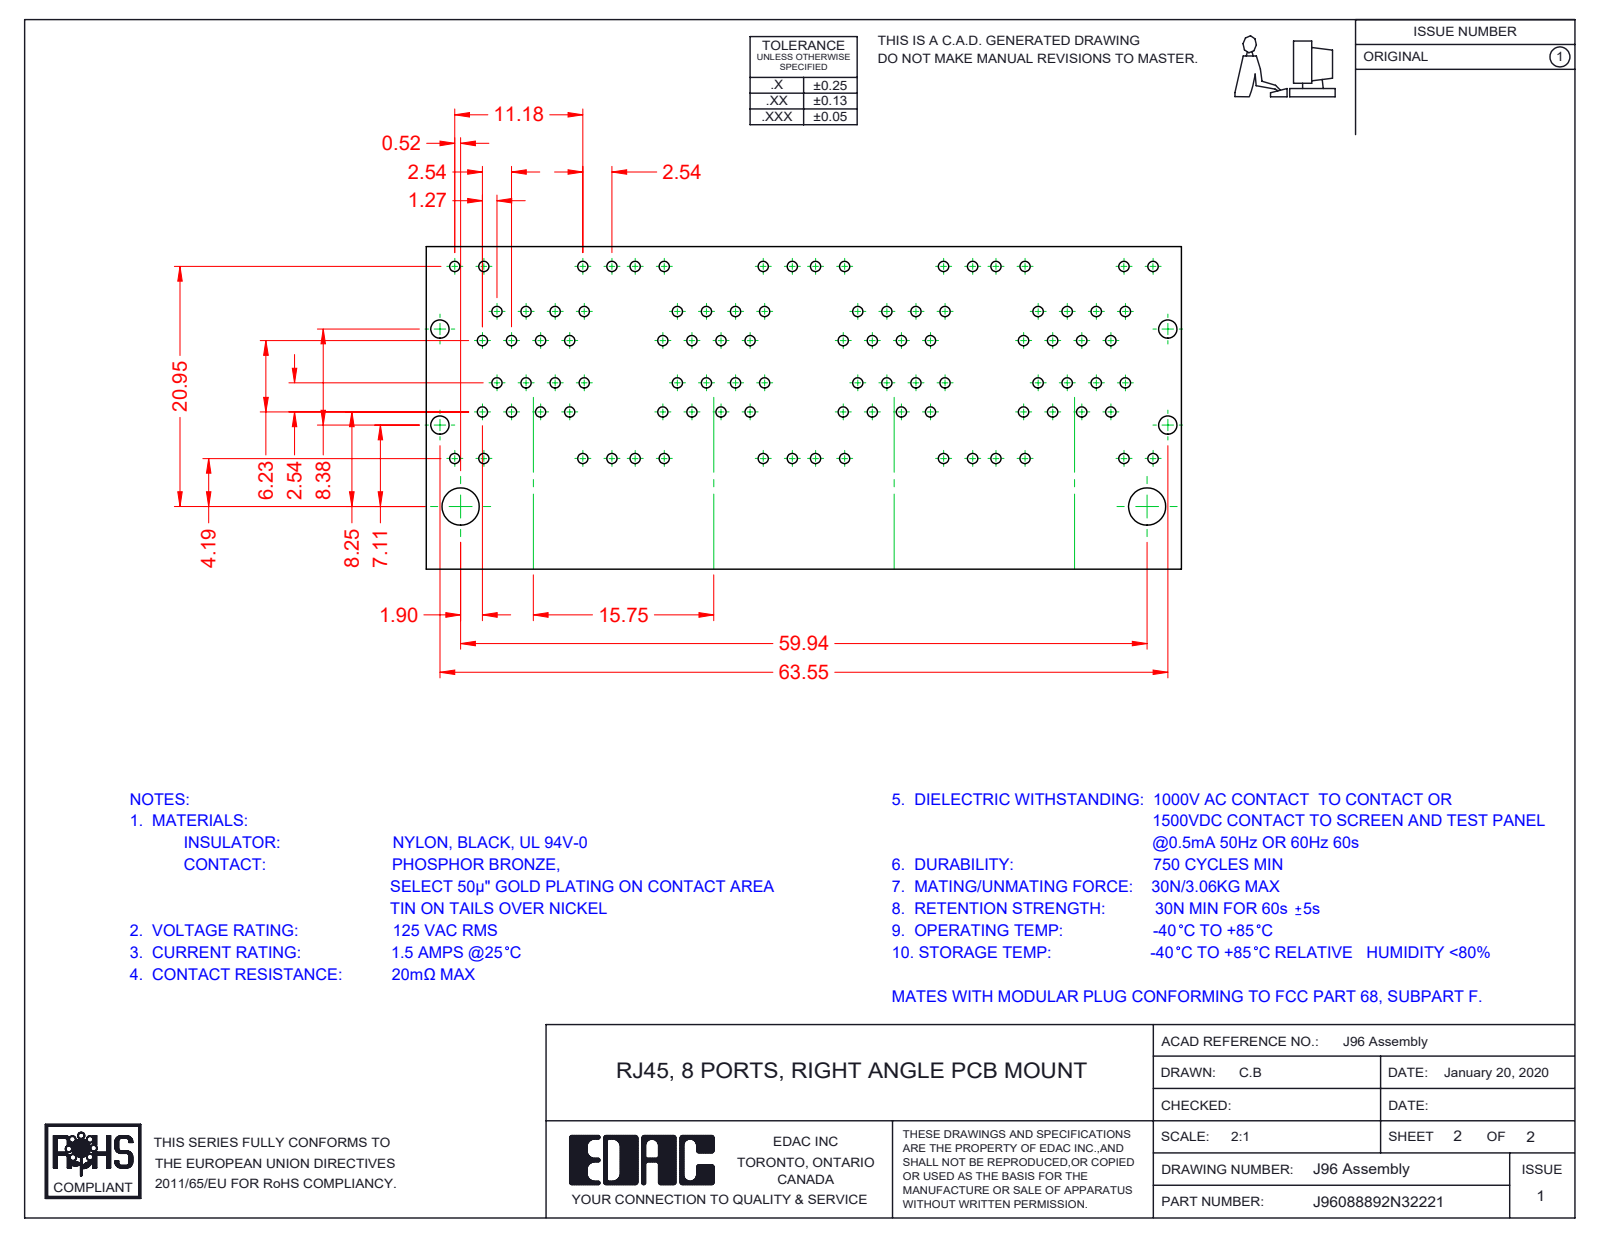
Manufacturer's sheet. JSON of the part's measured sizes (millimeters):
{"part_name": "96 Grounding_8 Ports; 96 LED RH Upper_2-Red; 96 Contact Lock Lower; 96 Insulator Insert (+8 more)", "step_written_by": "SolidWorks 2016 (CONFIG_CONTROL_DESIGN)", "units": "millimeters", "bodies": {"solids": 96, "faces": 7804, "planar": 6105, "cylindrical": 1388, "other": 311}, "overall_size": [67.35, 31.38, 28.68], "volume_mm3": 24149, "surface_area_mm2": 63596, "round_holes": [[1.7, 3]], "round_bosses_or_shafts": [[1.68, 3]], "partial_cylinders_radius": [[0.25, 124], [0.35, 73], [1, 72], [0.5, 49], [0.91, 32], [0.2, 27], [0.27, 14], [0.7, 11]], "face_to_face_distances": [15.75, 0.35, 9.95, 1.17, 1.6, 0.54, 9.98, 10.18, 12.67, 3.37], "hole_center_spacings": [15.75, 31.5]}
